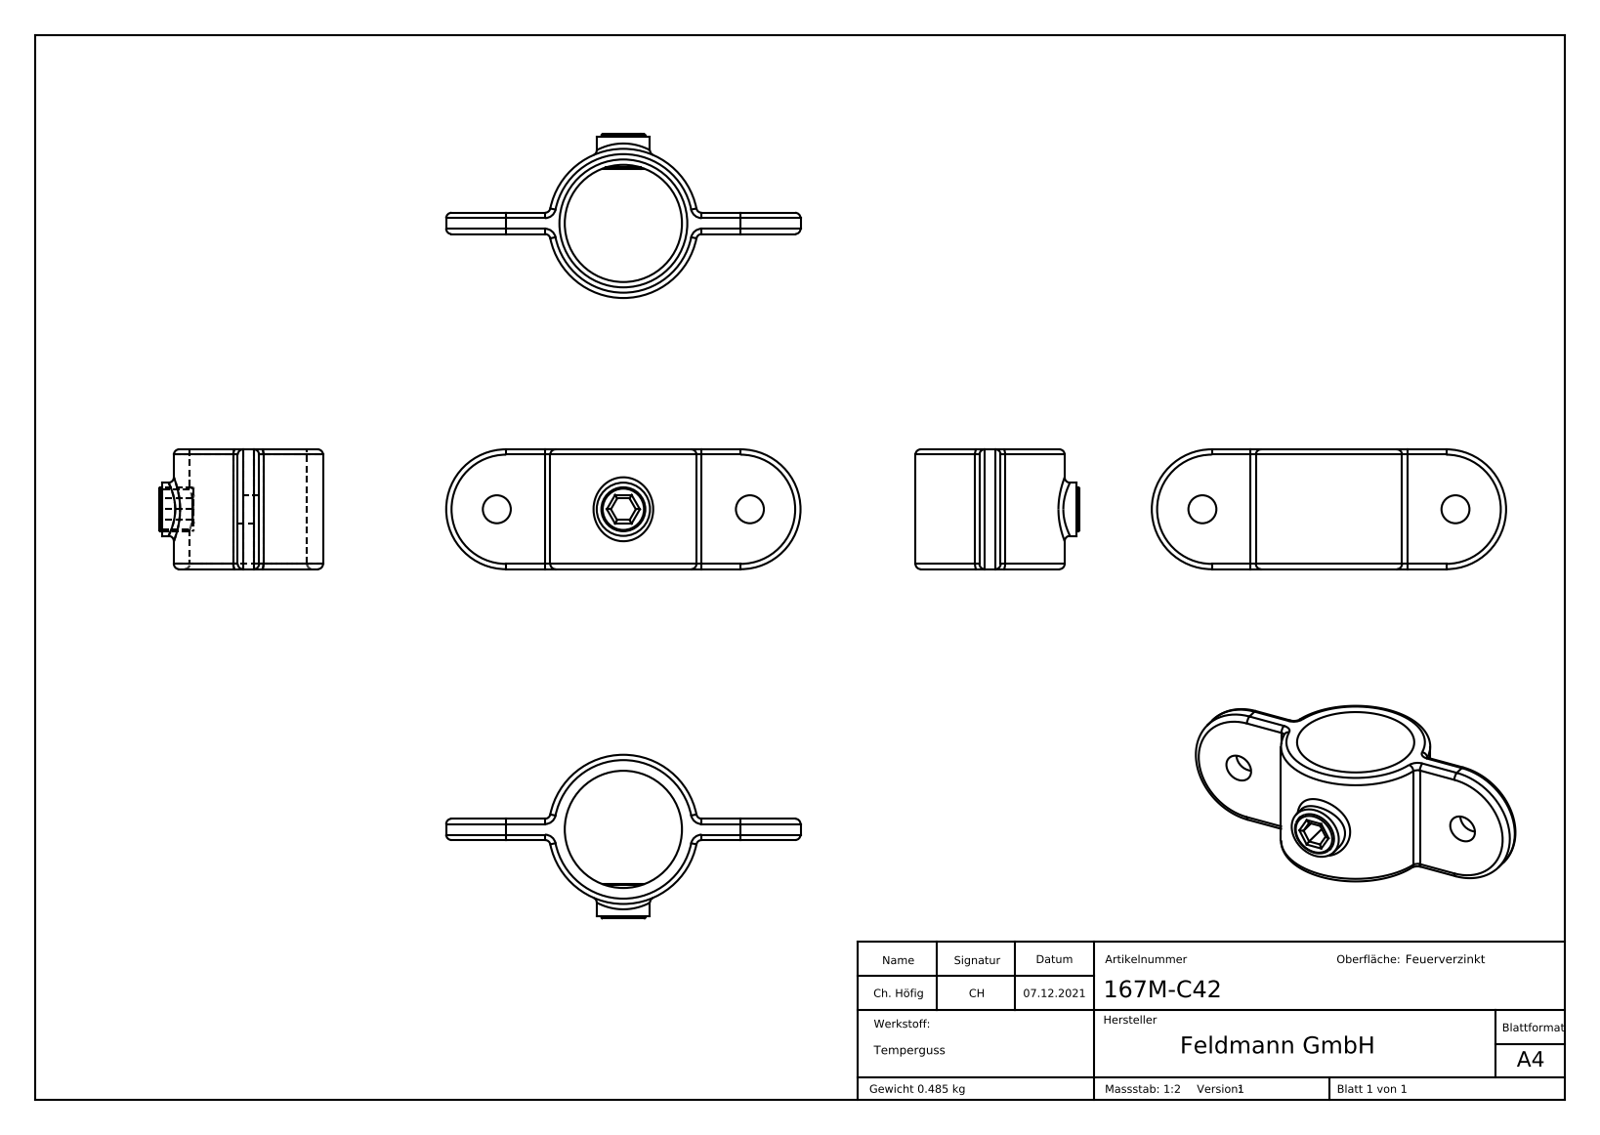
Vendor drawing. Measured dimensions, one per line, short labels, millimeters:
name: 167M-C42 Teil1; 167M-C42 Teil2; 167M-C42
written by: SolidWorks 2018 (CONFIG_CONTROL_DESIGN)
unit: mm
bodies: 2 solids, 69 faces (15 planar, 34 cylindrical, 20 other)
size: 133 × 61.5 × 45
volume: 66 336 mm³; area: 24 174 mm²
holes: 2× ⌀10.5, 1× ⌀15.25, 1× ⌀44
bosses: 1× ⌀56, 1× ⌀20, 1× ⌀16.5
rounds: 20× R2, 2× R22.5
face distances: 8, 45, 8.1, 36.5, 28.5, 18.45, 26.55, 24.5, 16.5, 12
hole spacings: 47.5, 95
